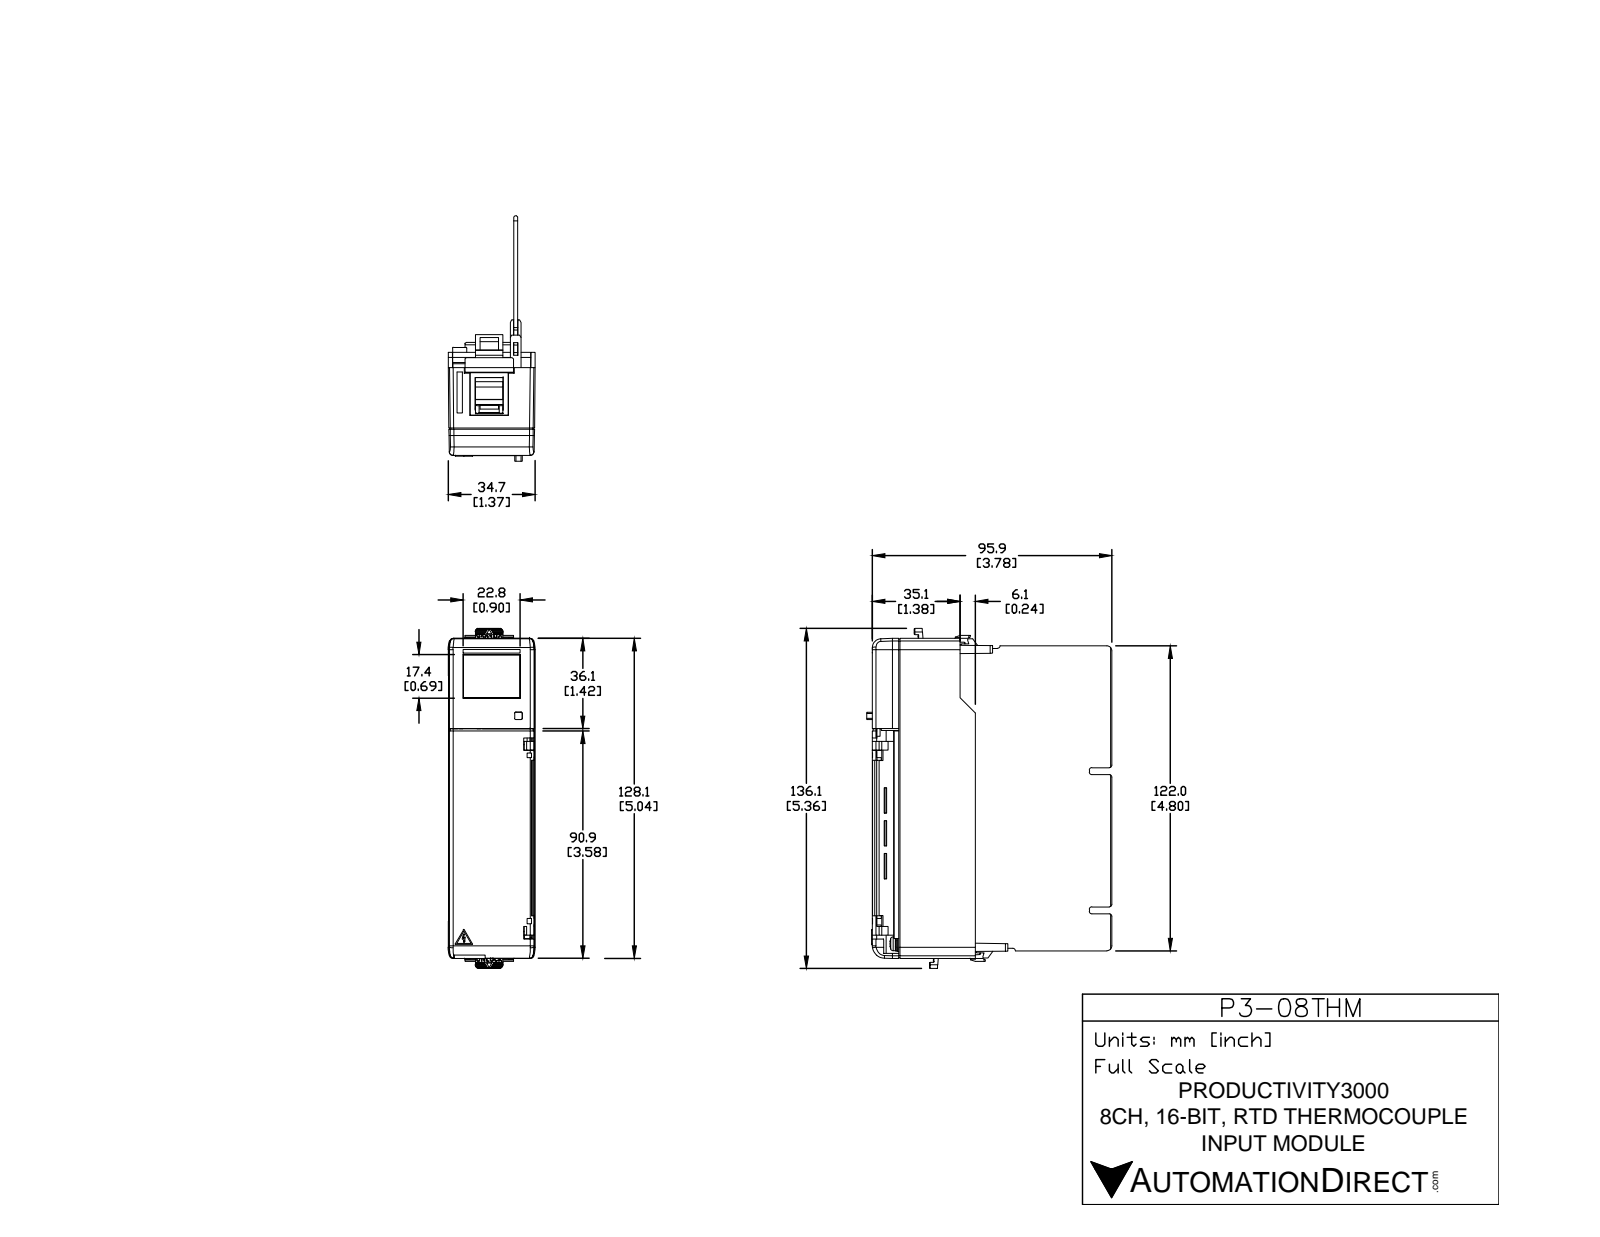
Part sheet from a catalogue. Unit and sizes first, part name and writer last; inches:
Units: inches
Overall size (bounding box): 5.357 × 3.865 × 1.37
Round holes (diameter × count): ⌀0.126 ×22, ⌀0.197 ×2, ⌀0.071 ×1
Round bosses / shafts (diameter × count): ⌀0.217 ×22, ⌀0.118 ×22, ⌀0.094 ×20, ⌀0.22 ×2, ⌀0.087 ×2, ⌀0.079 ×2, ⌀0.059 ×1
Partial cylindrical surfaces — rounded edges, fillets, slot ends (radius × count): R0.02 ×95, R0.039 ×33, R0.012 ×29, R0.066 ×22, R0.059 ×13, R0.079 ×6, R0.008 ×5, R0.004 ×4
Main face-to-face distances: 0.063, 0.067, 1.111, 1.044, 1.282, 0.874, 0.087, 0.311, 0.268, 0.209
Hole centre spacings: 0.342, 0.3, 0.545, 0.6, 0.811, 0.9, 1.094, 1.2
Volume: 6.185 in³ · Surface area: 116.8 in²
Bodies: 1 solid, 3823 faces (2833 planar, 744 cylindrical, 246 other)
Part name (STEP PRODUCT): P3-08THM
STEP written by: SolidWorks 2009 (CONFIG_CONTROL_DESIGN)
